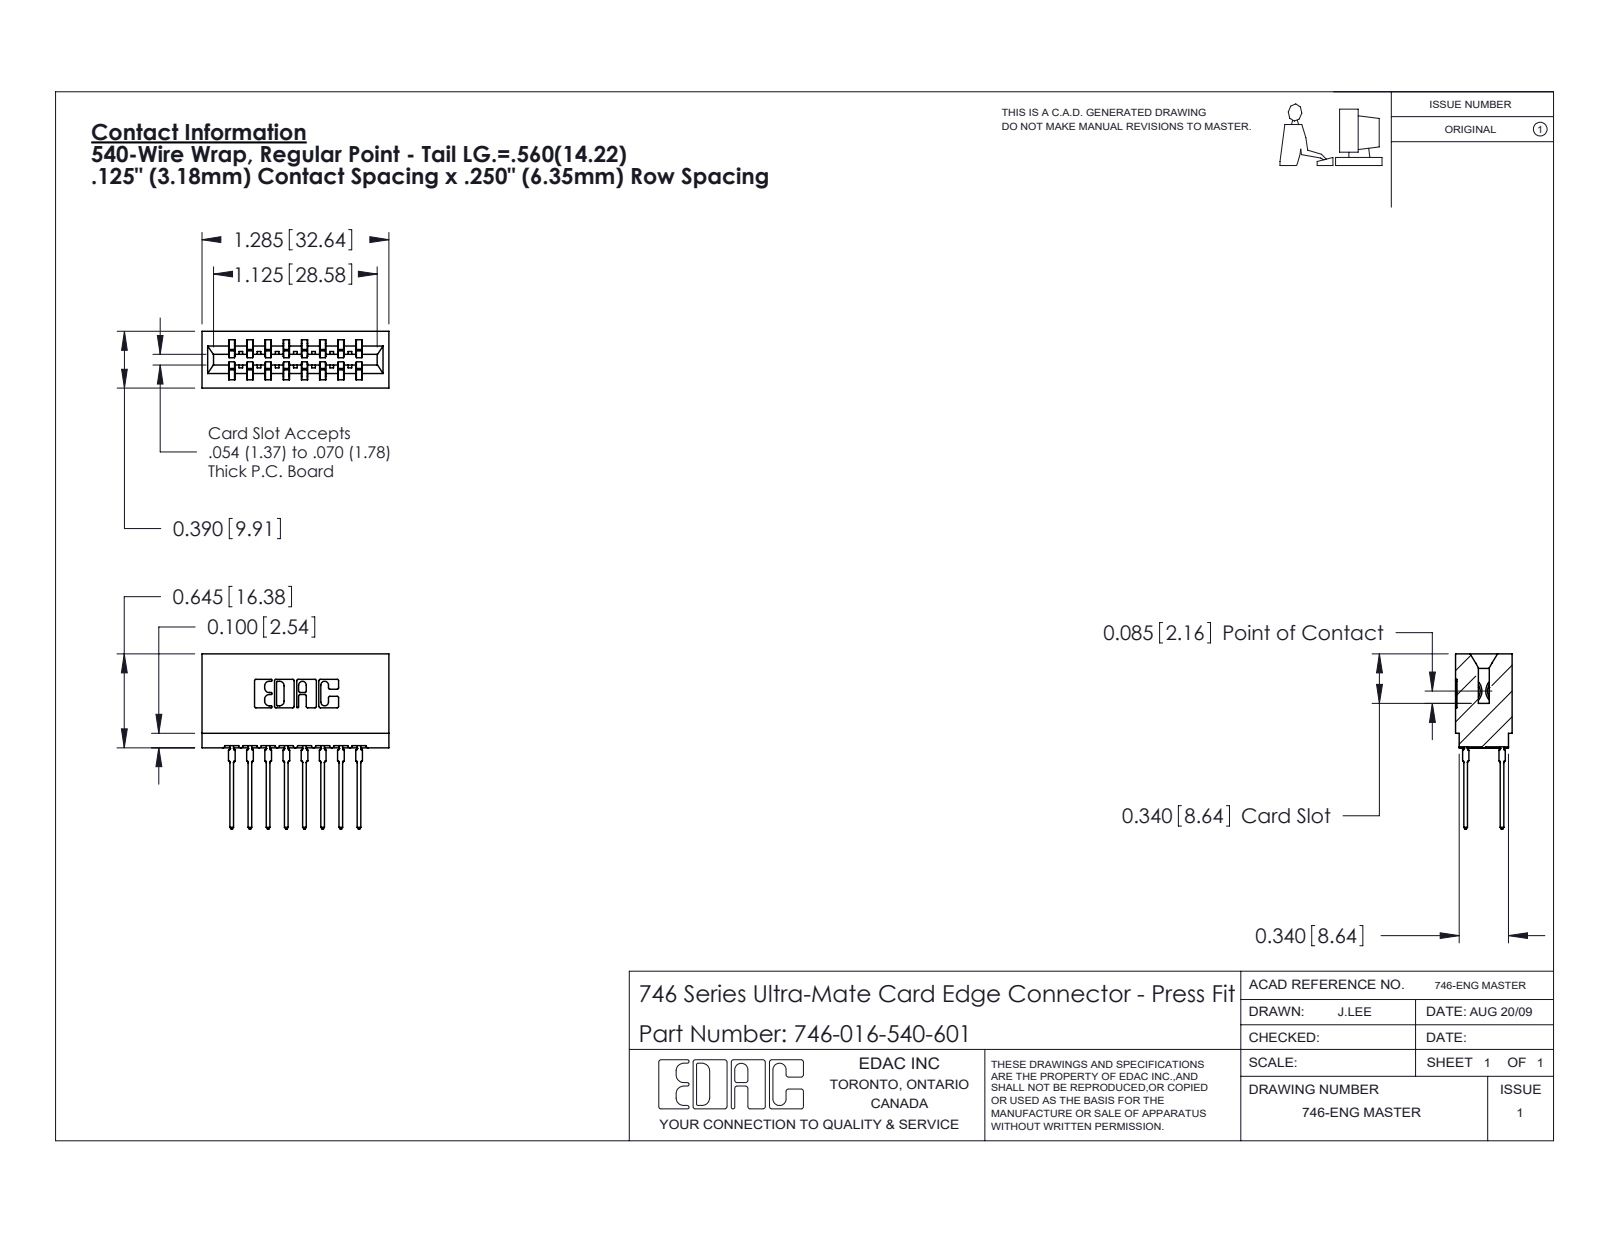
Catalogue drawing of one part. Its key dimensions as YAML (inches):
part_name: "746-292-001_540; 746 Part_.340 Slot Depth - 01; 746-016-540-601"
step_written_by: "SolidWorks 2020 (CONFIG_CONTROL_DESIGN)"
units: inches
bodies: {solids: 17, faces: 1529, planar: 791, cylindrical: 322, other: 416}
overall_size: [1.285, 1.204, 0.39]
volume: 0.244
surface_area: 8.47
partial_cylinders:
  - {radius: 0.021, count: 32}
  - {radius: 0.01, count: 22}
  - {radius: 0.015, count: 9}
  - {radius: 0.005, count: 8}
  - {radius: 0.011, count: 8}
  - {radius: 0.007, count: 6}
  - {radius: 0.031, count: 6}
  - {radius: 0.026, count: 3}
face_to_face_distances: [0.25, 0.333, 0.057, 0.042, 0.125, 0.5, 0.292, 0.375, 0.208, 0.125]
